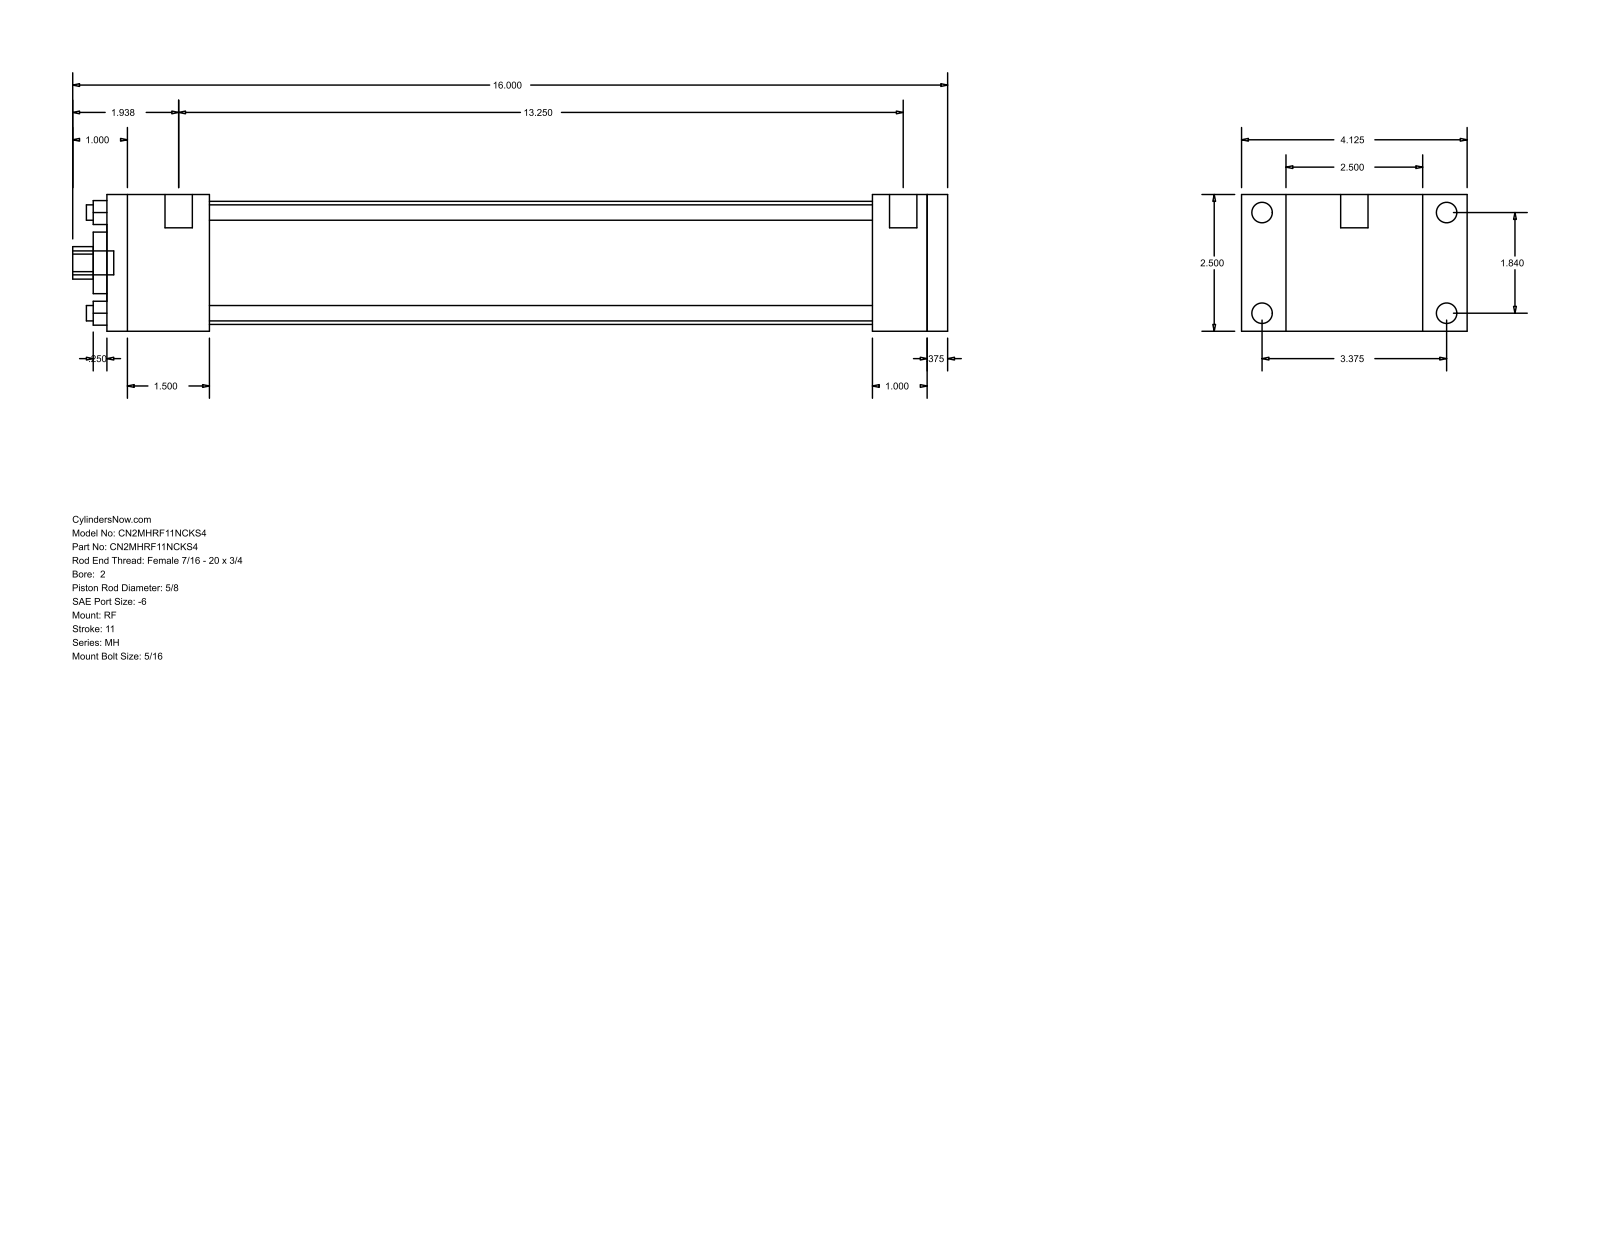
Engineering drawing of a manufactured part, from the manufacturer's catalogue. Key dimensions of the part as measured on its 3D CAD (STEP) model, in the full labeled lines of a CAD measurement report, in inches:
Part name (STEP PRODUCT): MH_RF__0200_0.625
STEP written by: GSSL Pune (CONFIG_CONTROL_DESIGN)
Units: inches
Bodies: 0 solids, 92 faces (64 planar, 28 cylindrical, 0 other)
Overall size (bounding box): 16 × 4.125 × 2.5
Round holes (diameter × count): ⌀0.281 ×4, ⌀0.625 ×1, ⌀1.125 ×1, ⌀2.25 ×1
Round bosses / shafts (diameter × count): ⌀0.375 ×4, ⌀0.219 ×4, ⌀0.5 ×2, ⌀0.437 ×1
Partial cylindrical surfaces — rounded edges, fillets, slot ends (radius × count): R0.297 ×1
Main face-to-face distances: 2.5, 15.375, 0.375, 15, 1, 1.875, 14, 12.125, 13.125, 13.5
Hole centre spacings: 1.301, 1.84, 2.602
